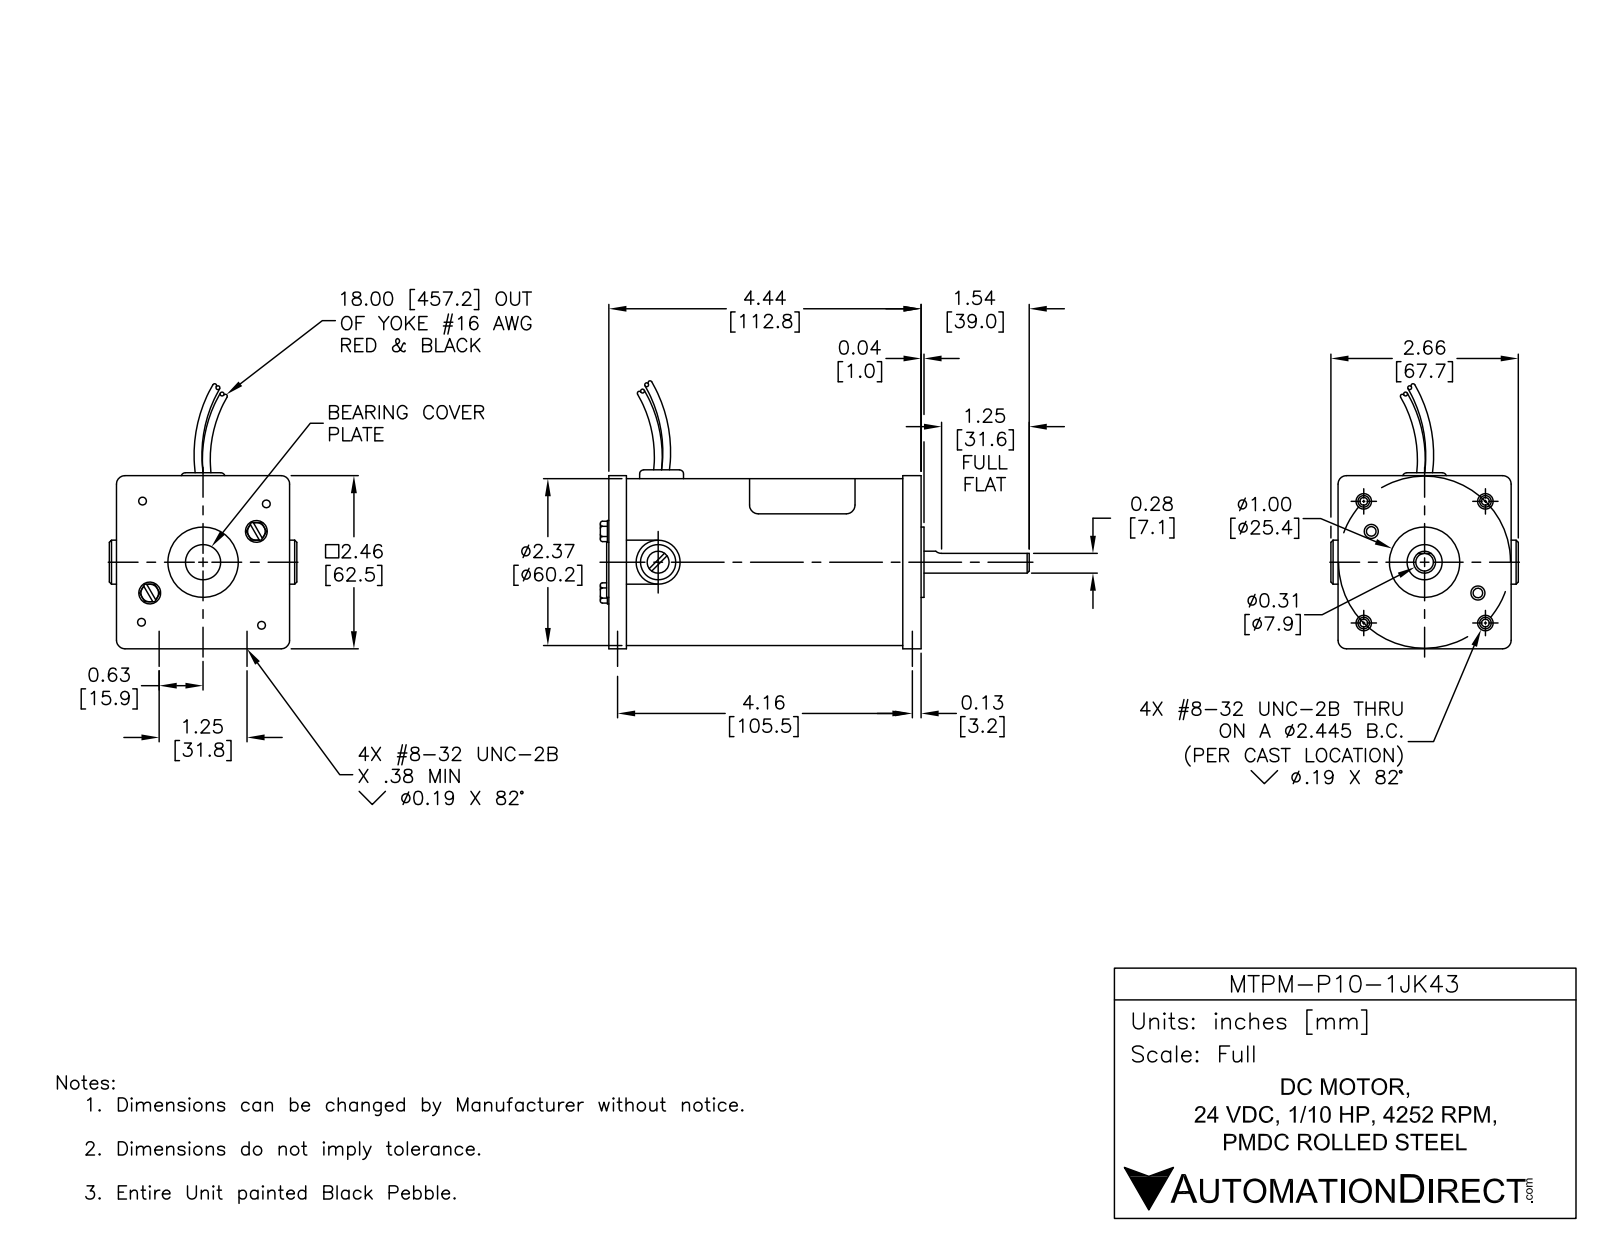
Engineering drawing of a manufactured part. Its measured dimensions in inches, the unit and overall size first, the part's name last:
Units: inches
Overall size (bounding box): 6.104 × 3.71 × 2.602
Round holes (diameter × count): ⌀0.063 ×4, ⌀0.156 ×2, ⌀0.25 ×1, ⌀0.562 ×1, ⌀1 ×1, ⌀2.25 ×1
Round bosses / shafts (diameter × count): ⌀0.312 ×4, ⌀0.1 ×2, ⌀2.375 ×1, ⌀0.625 ×1, ⌀0.625 ×1
Main face-to-face distances: 0.25, 4.194, 3.944, 4.444, 2.46, 4.481, 4.231, 0.287, 0.037, 0.25
Hole centre spacings: 1.223, 1.729, 0.44, 0.875, 1.306, 1.678, 2.08, 2.445
Volume: 5.522 in³ · Surface area: 104 in²
Bodies: 20 solids, 150 faces (71 planar, 76 cylindrical, 3 other)
Part name (STEP PRODUCT): MTPM-P10-1JK43
STEP written by: SolidWorks 2013 (AUTOMOTIVE_DESIGN)
